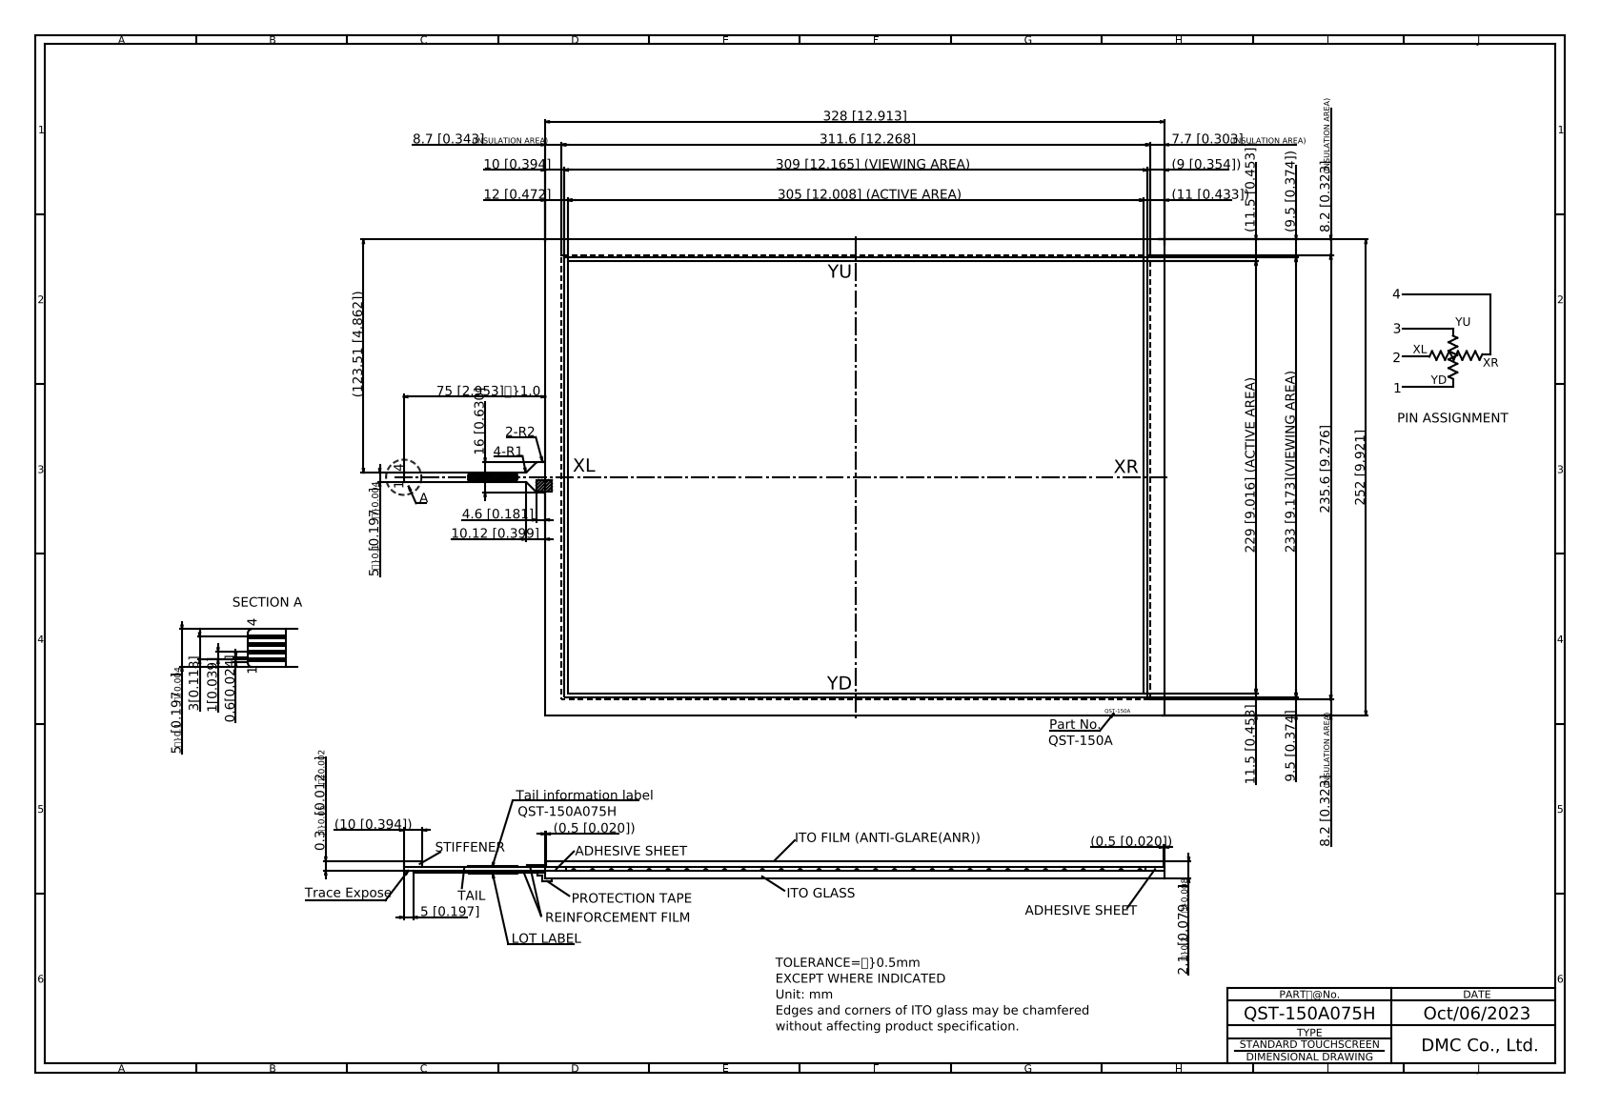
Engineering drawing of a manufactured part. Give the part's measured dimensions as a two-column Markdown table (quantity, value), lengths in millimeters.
| quantity | value |
| --- | --- |
| part name | QST-150A075H |
| STEP written by | Autodesk Inventor 2020 (CONFIG_CONTROL_DESIGN) |
| units | millimeters |
| bodies | 1 solid, 51 faces (45 planar, 6 cylindrical, 0 other) |
| overall size | 468.6 × 352.8 × 2.2 |
| volume | 173 420 mm³ |
| surface area | 168 897 mm² |
| partial cylindrical surfaces (radius × count) | 0.5 × 2, 1 × 2, 2 × 2 |
| main face-to-face distances | 2.1, 2, 252, 328, 1.8, 1.9, 9.5, 242.5, 11.5, 240.5 |
